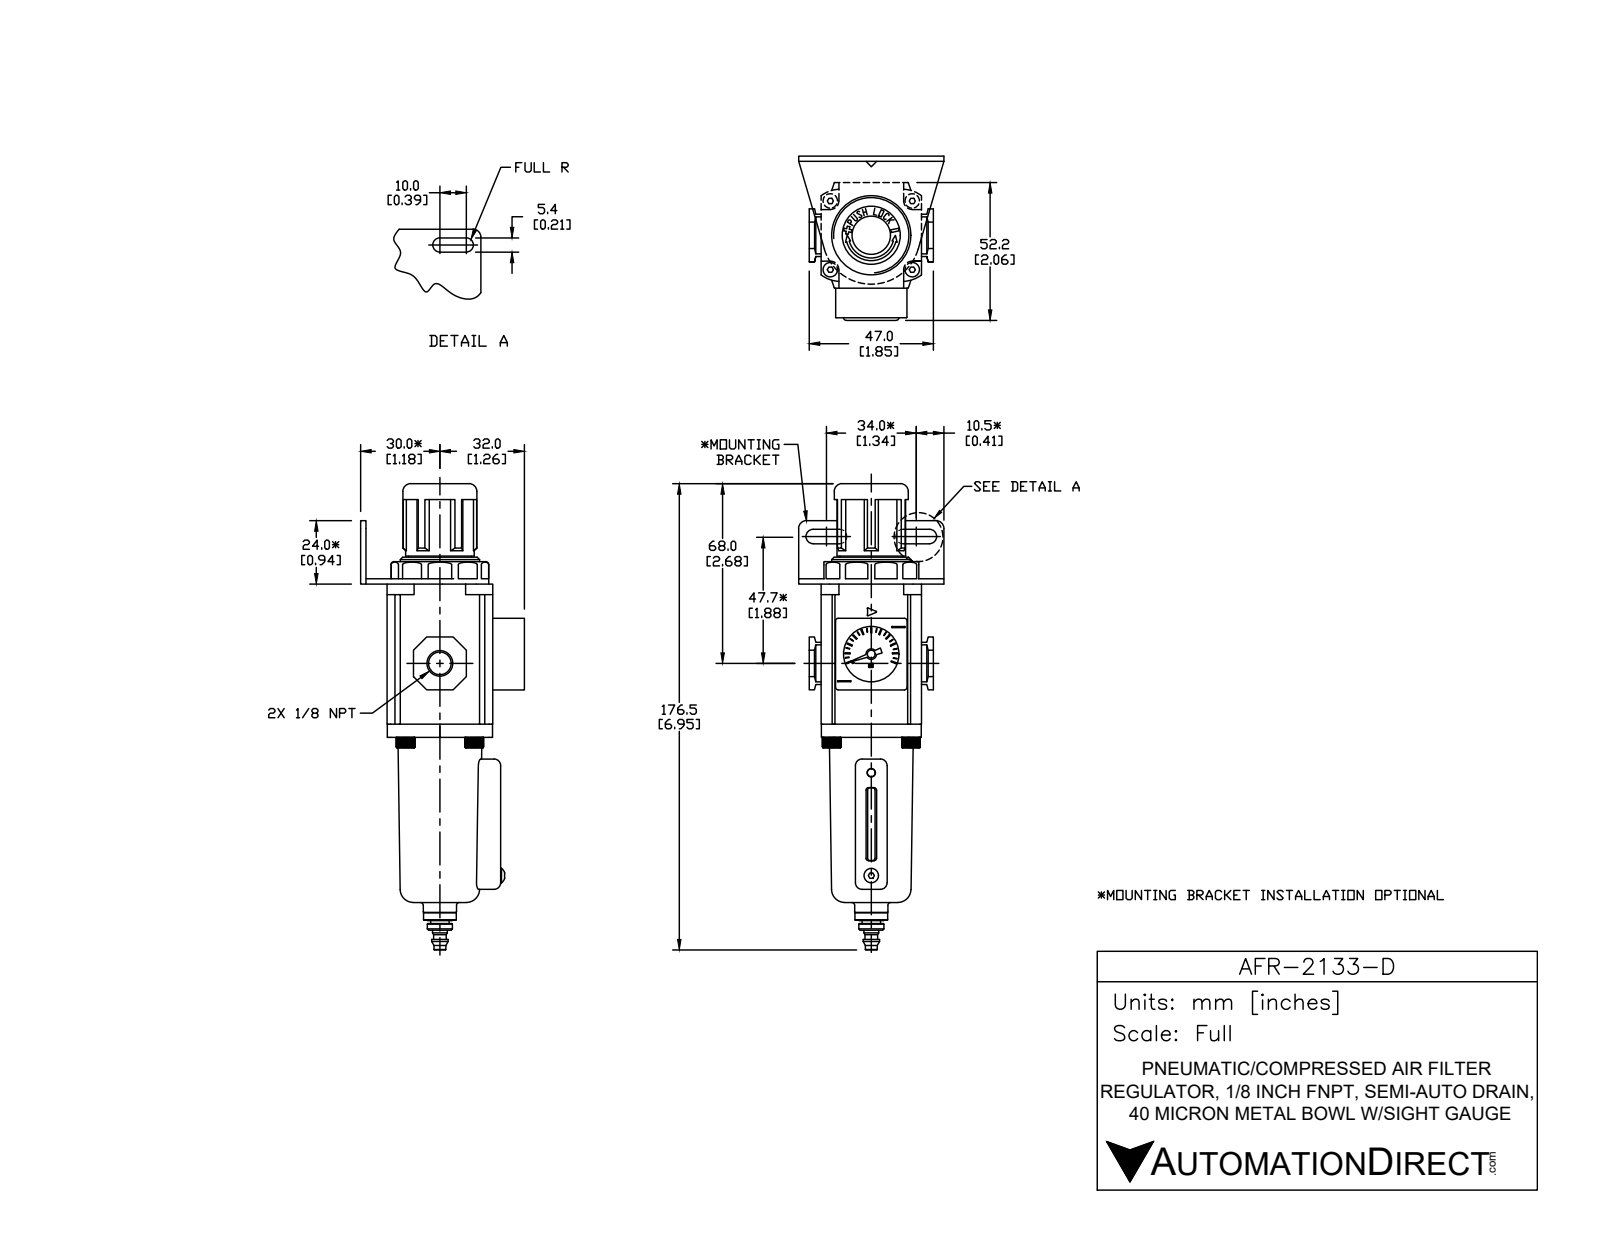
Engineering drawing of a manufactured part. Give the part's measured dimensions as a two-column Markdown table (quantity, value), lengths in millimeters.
| quantity | value |
| --- | --- |
| part name | AFR-2133-D |
| STEP written by | SolidWorks 2015 (CONFIG_CONTROL_DESIGN) |
| units | millimeters |
| bodies | 16 solids, 657 faces (397 planar, 190 cylindrical, 70 other) |
| overall size | 176.5 × 62 × 55 |
| volume | 170 865 mm³ |
| surface area | 42 753 mm² |
| round holes (diameter × count) | 3 × 7, 2 × 1, 8.43 × 1, 21 × 1, 22 × 1, 30 × 1 |
| round bosses / shafts (diameter × count) | 5.5 × 6, 7 × 4, 2.7 × 2, 28 × 1, 26 × 1, 23.8 × 1, 14 × 1, 12.6 × 1 |
| partial cylindrical surfaces (radius × count) | 1 × 16, 0.3 × 12, 1.2 × 10, 1.3 × 8, 2.5 × 8, 3.25 × 6, 0.5 × 4, 2.75 × 4 |
| main face-to-face distances | 2, 53, 55, 40, 38, 10, 39, 1, 50, 9 |
| hole center spacings | 20.23, 14.5, 26, 31, 40.46, 28.99 |
